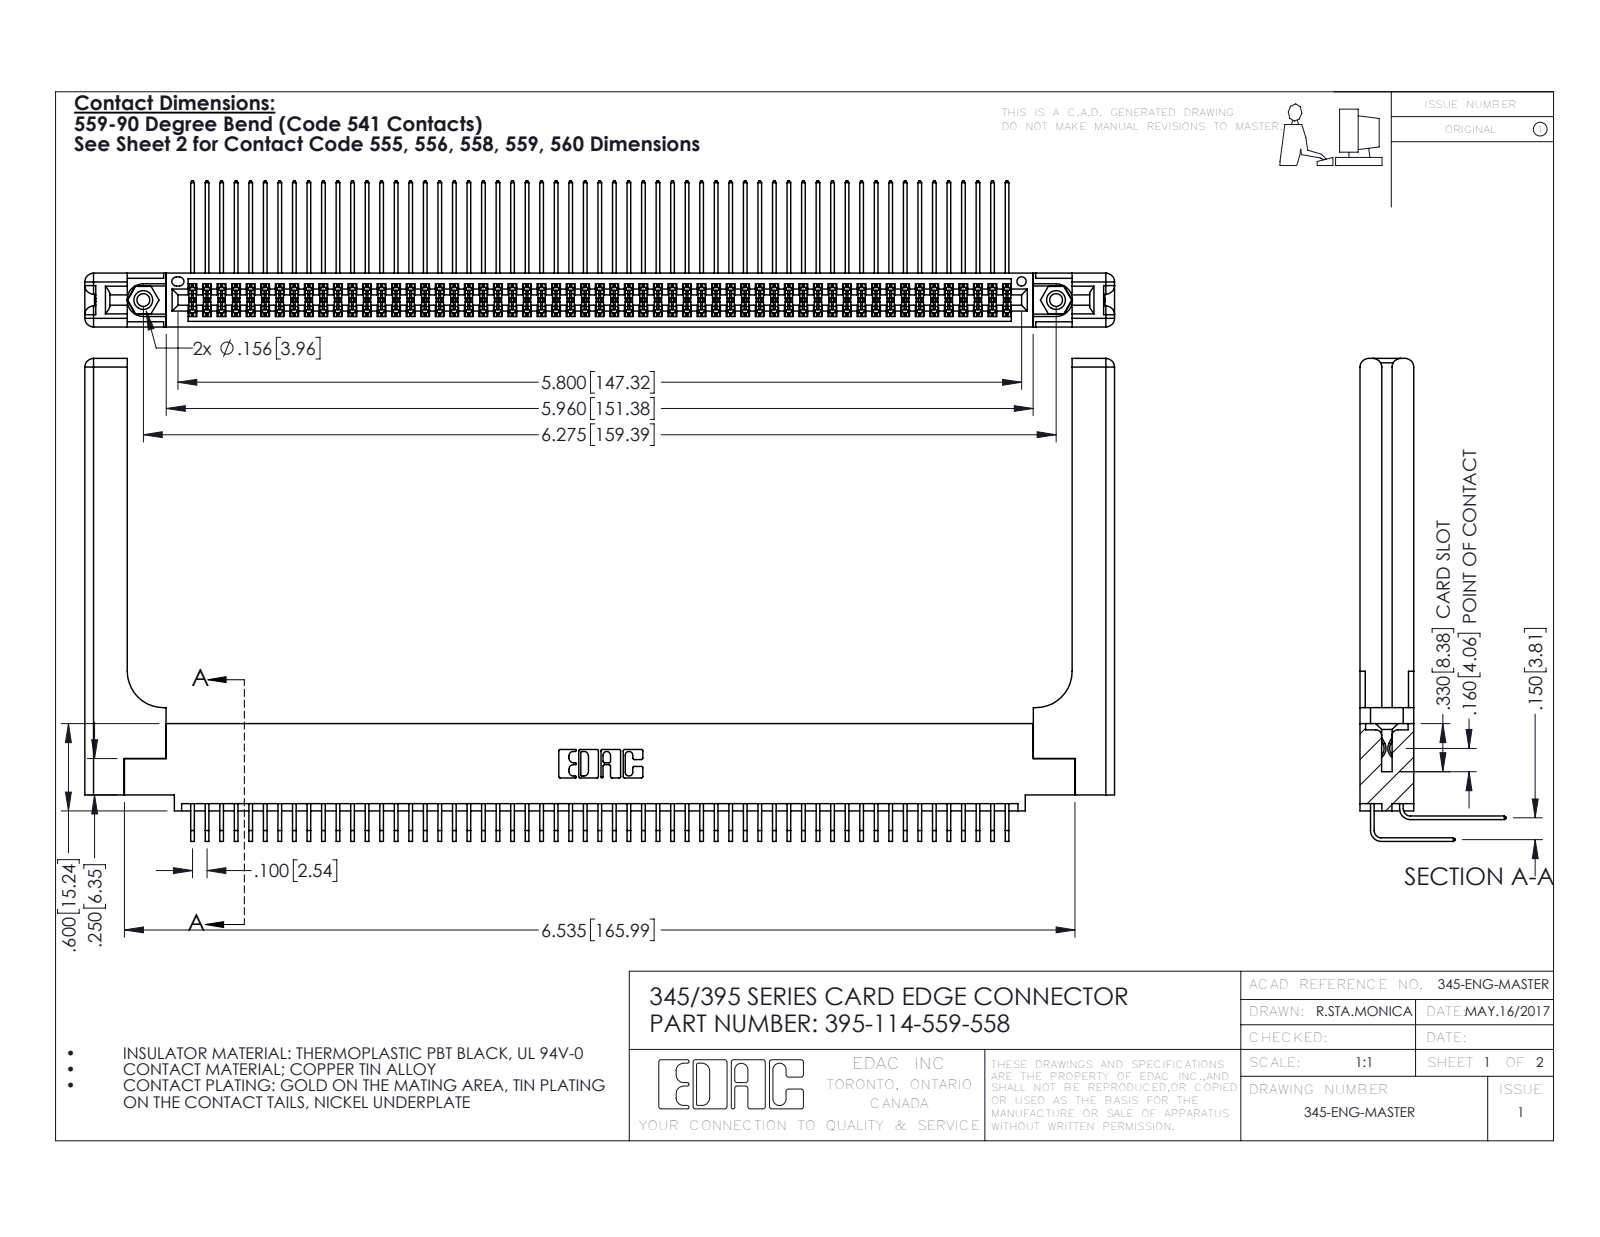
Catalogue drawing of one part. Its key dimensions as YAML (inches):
part_name: "345-250-001_345-250-001-102; 345 Part_0.110 Offset - 0.156 Dia-TH; 345-292-001_558 559 Tail - 1; 395-114-559-558 (+2 more)"
step_written_by: "SolidWorks 2016 (CONFIG_CONTROL_DESIGN)"
units: inches
bodies: {solids: 119, faces: 6314, planar: 4222, cylindrical: 2032, other: 60}
overall_size: [7.079, 3.319, 1.005]
volume: 1.627
surface_area: 54.91
round_holes:
  - {diameter: 0.089, count: 2}
  - {diameter: 0.125, count: 2}
  - {diameter: 0.156, count: 2}
  - {diameter: 0.064, count: 1}
round_bosses_or_shafts:
  - {diameter: 0.155, count: 2}
partial_cylinders:
  - {radius: 0.006, count: 171}
  - {radius: 0.01, count: 22}
  - {radius: 0.06, count: 16}
  - {radius: 0.007, count: 6}
  - {radius: 0.031, count: 6}
  - {radius: 0.026, count: 3}
  - {radius: 0.014, count: 2}
  - {radius: 0.019, count: 2}
face_to_face_distances: [0.072, 0.298, 0.37, 0.098, 0.272, 0.025, 0.2, 0.225, 0.175, 0.15]
hole_center_spacings: [0.27, 6.039, 6.275]
